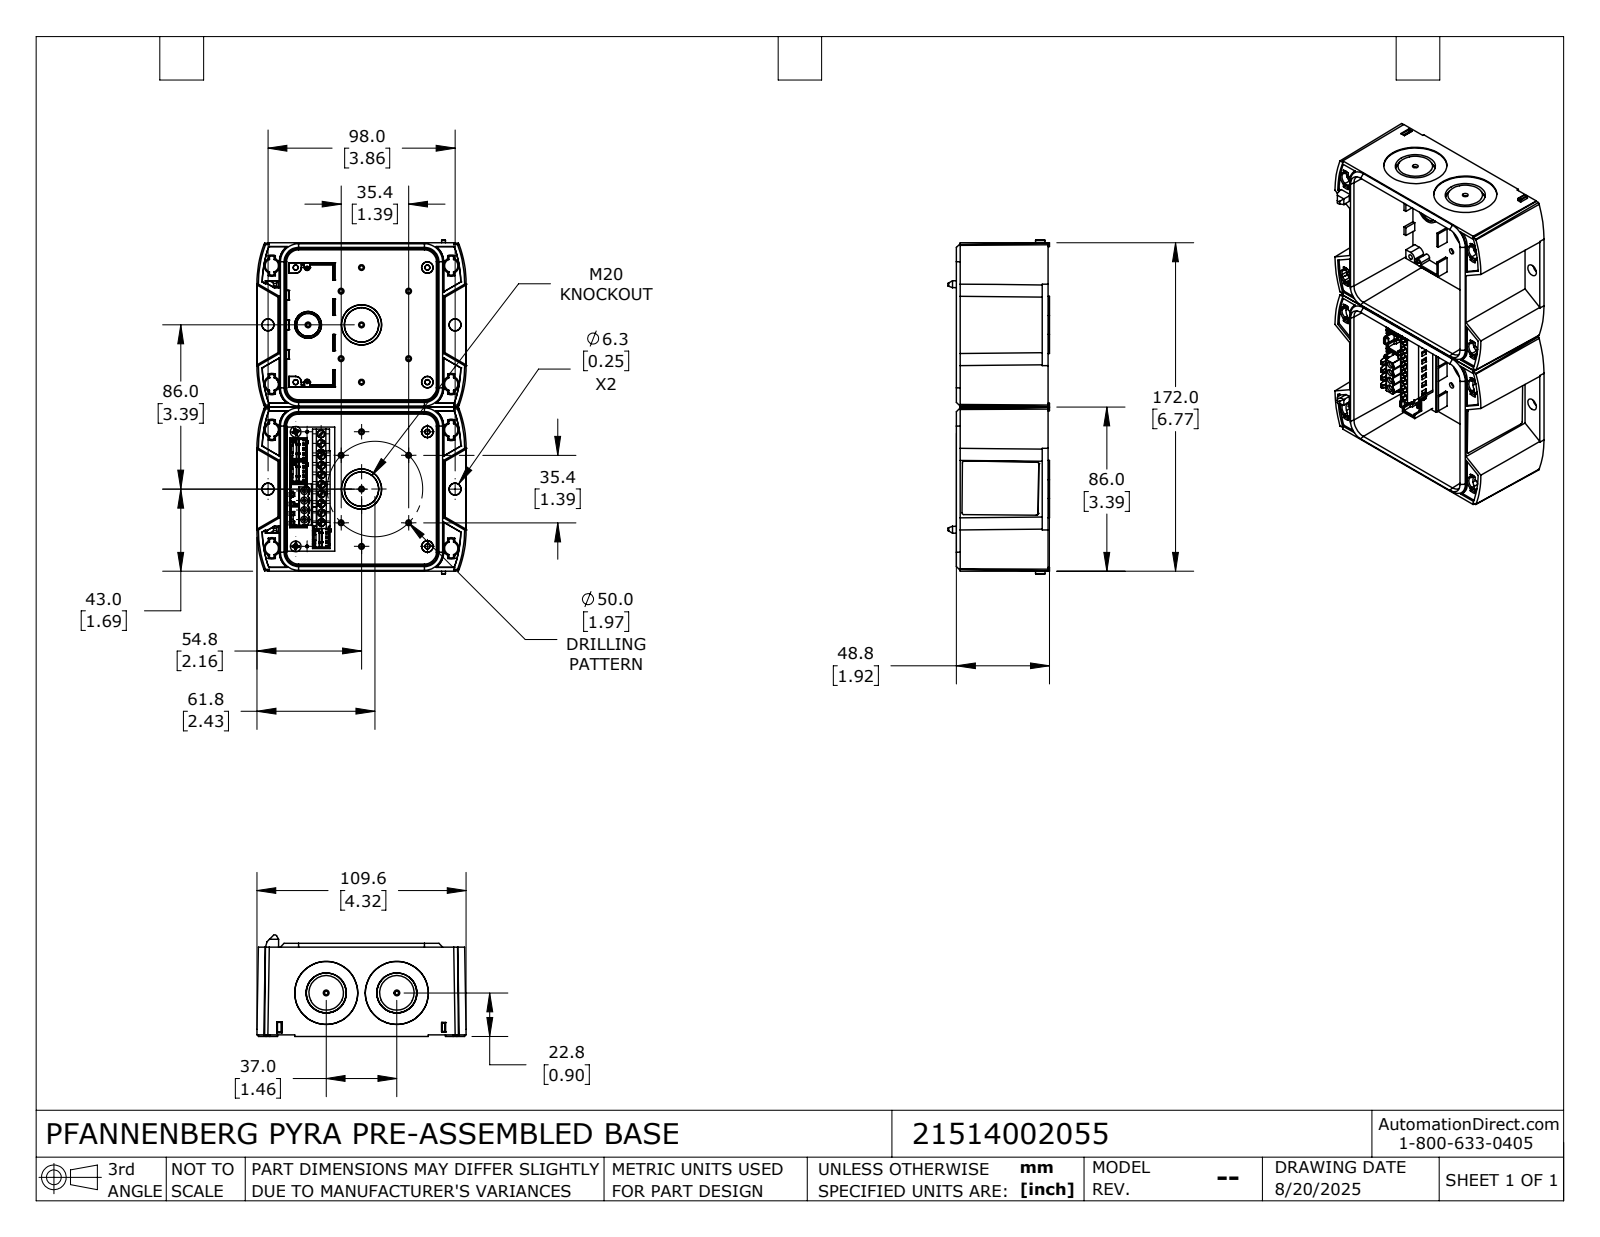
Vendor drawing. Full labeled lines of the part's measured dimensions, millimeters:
Part name (STEP PRODUCT): 21514002055
STEP written by: SolidWorks 2024 (CONFIG_CONTROL_DESIGN)
Units: millimetres
Bodies: 18 solids, 2800 faces (1949 planar, 387 cylindrical, 464 other)
Overall size (bounding box): 175 × 109.61 × 53.28
Volume: 201 488 mm³ · Surface area: 155 481 mm²
Round holes (diameter × count): ⌀4 ×18, ⌀1 ×10, ⌀1.4 ×10, ⌀1.9 ×5, ⌀1.8 ×4, ⌀2.3 ×4, ⌀3.6 ×4, ⌀1.5 ×2, ⌀3 ×2
Round bosses / shafts (diameter × count): ⌀3.8 ×18, ⌀1.8 ×5, ⌀5.6 ×2, ⌀2.9 ×2
Partial cylindrical surfaces — rounded edges, fillets, slot ends (radius × count): R0.3 ×32, R1 ×15, R0.4 ×14, R0.5 ×10, R2.9 ×5, R9 ×3
Main face-to-face distances: 86, 3, 83, 85.5, 6.5, 9.5, 0.5, 74.47, 11, 171.5
Hole centre spacings: 5, 10, 15, 11, 16, 20, 21, 6.01
